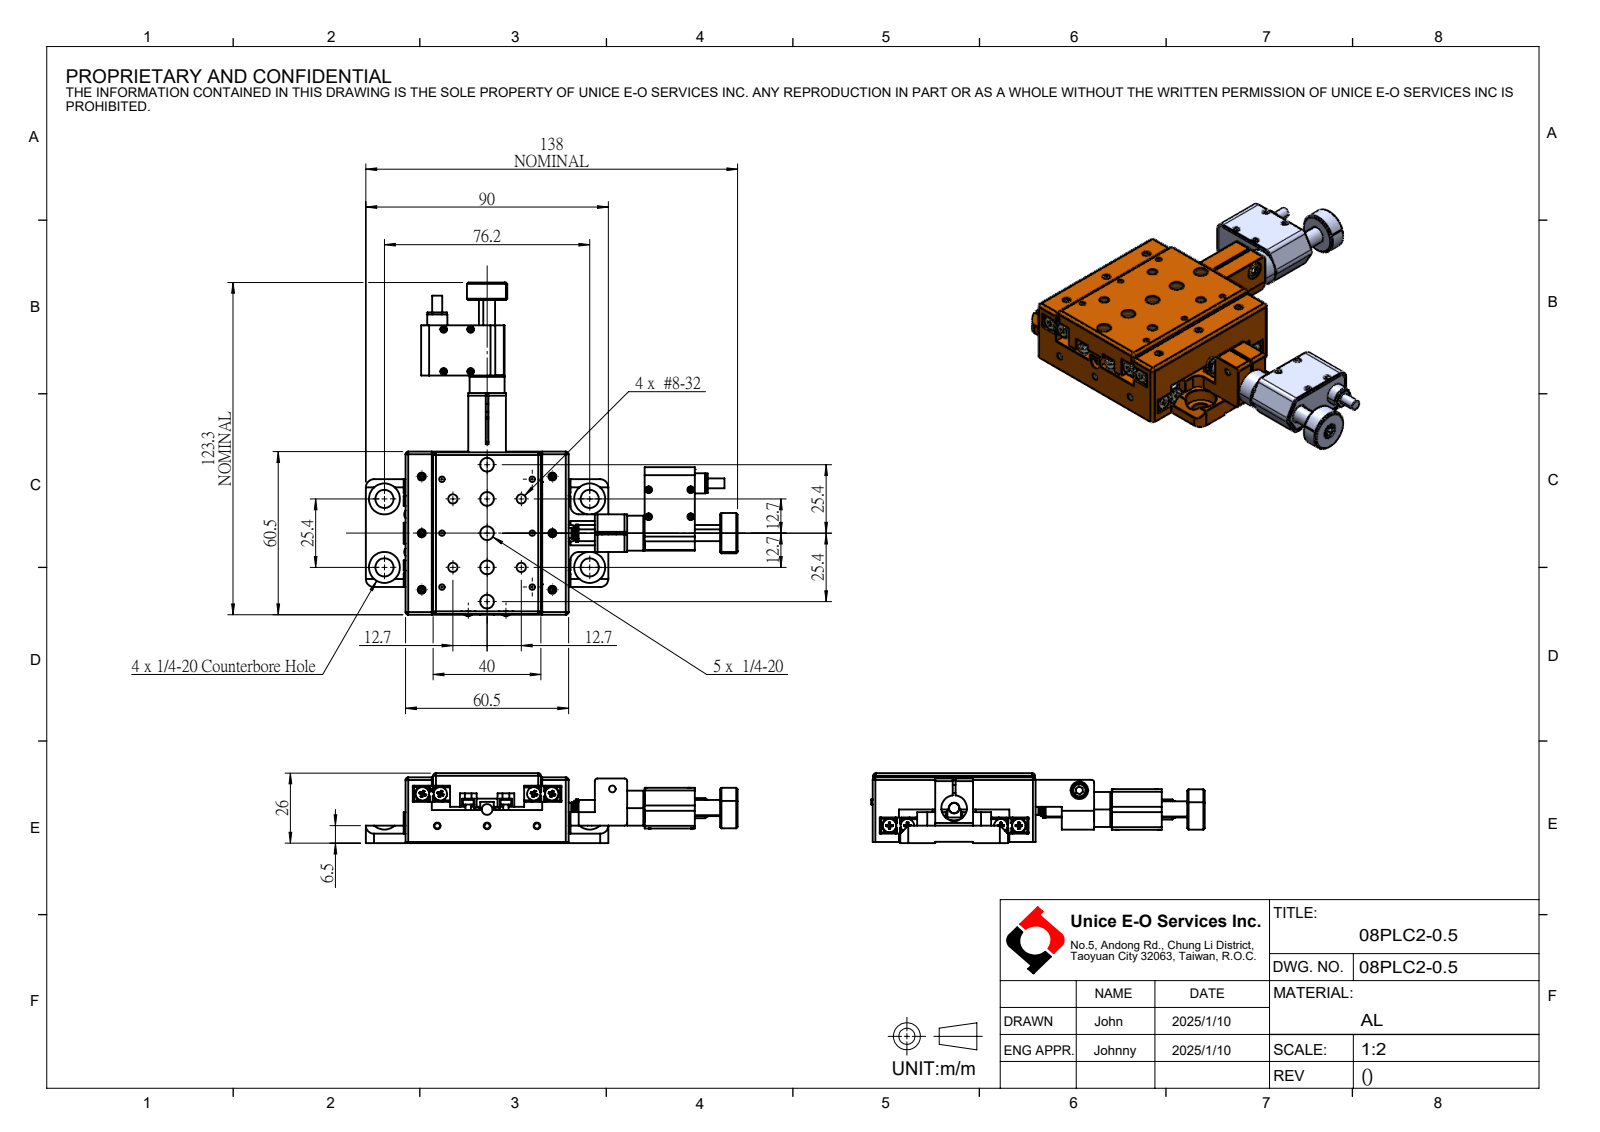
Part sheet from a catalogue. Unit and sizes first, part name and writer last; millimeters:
Units: millimetres
Overall size (bounding box): 138.02 × 123.82 × 26
Round holes (diameter × count): ⌀2.5 ×16, ⌀2.05 ×12, ⌀5.11 ×5, ⌀2 ×4, ⌀3.45 ×4, ⌀6.76 ×4, ⌀11.51 ×4, ⌀1.6 ×2, ⌀5.6 ×2, ⌀6.5 ×2, ⌀7.5 ×2, ⌀9.5 ×2
Round bosses / shafts (diameter × count): ⌀5 ×9, ⌀2 ×8, ⌀4 ×6, ⌀15 ×2, ⌀6.4 ×2, ⌀6 ×2, ⌀3.7 ×2
Partial cylindrical surfaces — rounded edges, fillets, slot ends (radius × count): R1 ×20, R3 ×10, R2 ×6, R1.5 ×4, R0.7 ×3, R2.5 ×1, R7 ×1
Main face-to-face distances: 6, 3, 6.75, 3.1, 11.8, 9, 13.5, 16.5, 0.5, 14.8
Hole centre spacings: 25.4, 40.16, 8.35, 12.7, 13.33, 17.06, 17.96, 20
Bodies: 0 solids, 1200 faces (714 planar, 278 cylindrical, 208 other)
Part name (STEP PRODUCT): 08PLC2-0.5
STEP written by: SolidWorks 2024 (CONFIG_CONTROL_DESIGN)
